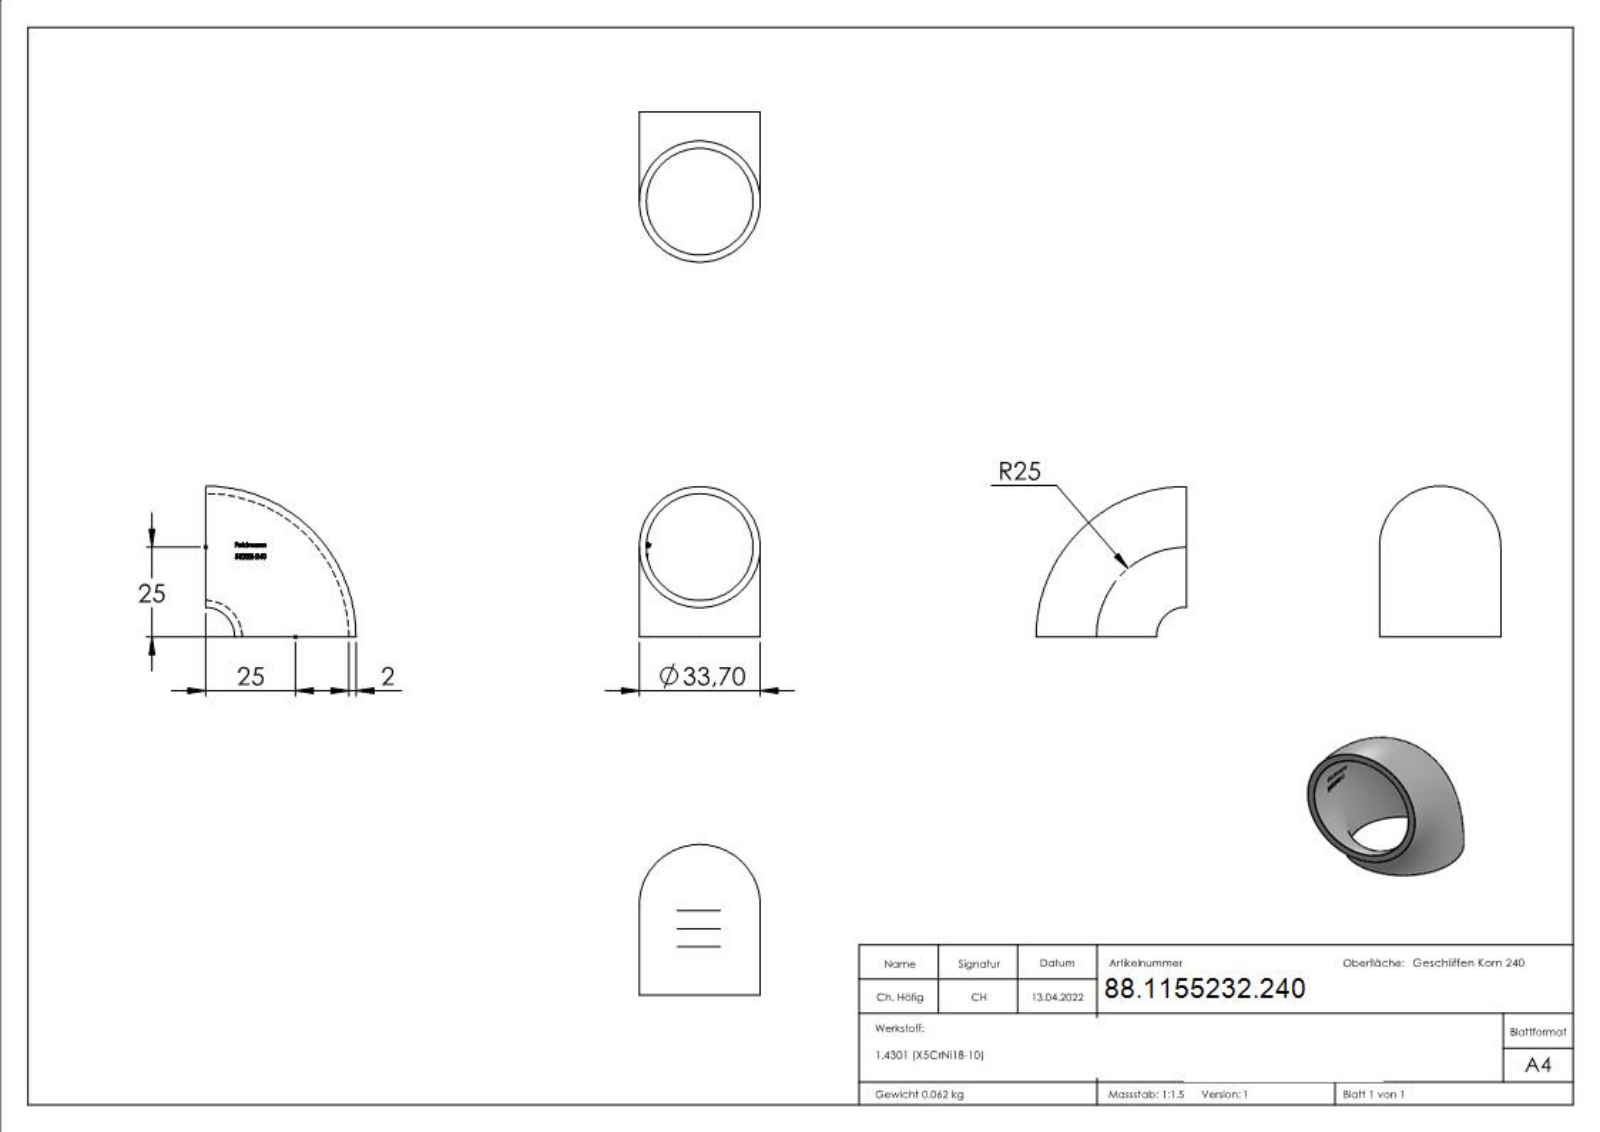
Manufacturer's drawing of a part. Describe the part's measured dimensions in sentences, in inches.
The part is named "55232-240". Its 3-D file was written by "SolidWorks 2018 (CONFIG_CONTROL_DESIGN)". It is 1 solid with 235 faces: 106 planar, 0 cylindrical and 129 other. Overall it measures 1.648 by 1.648 by 1.327 inches. Its volume is 0.477 cubic inches and its surface area 12.76 square inches. The main face-to-face distances are 0.117, 0.015, 0.858, 0.052, 0.044, 0.161, 0.144, 0.047, 0.129, 0.121.
